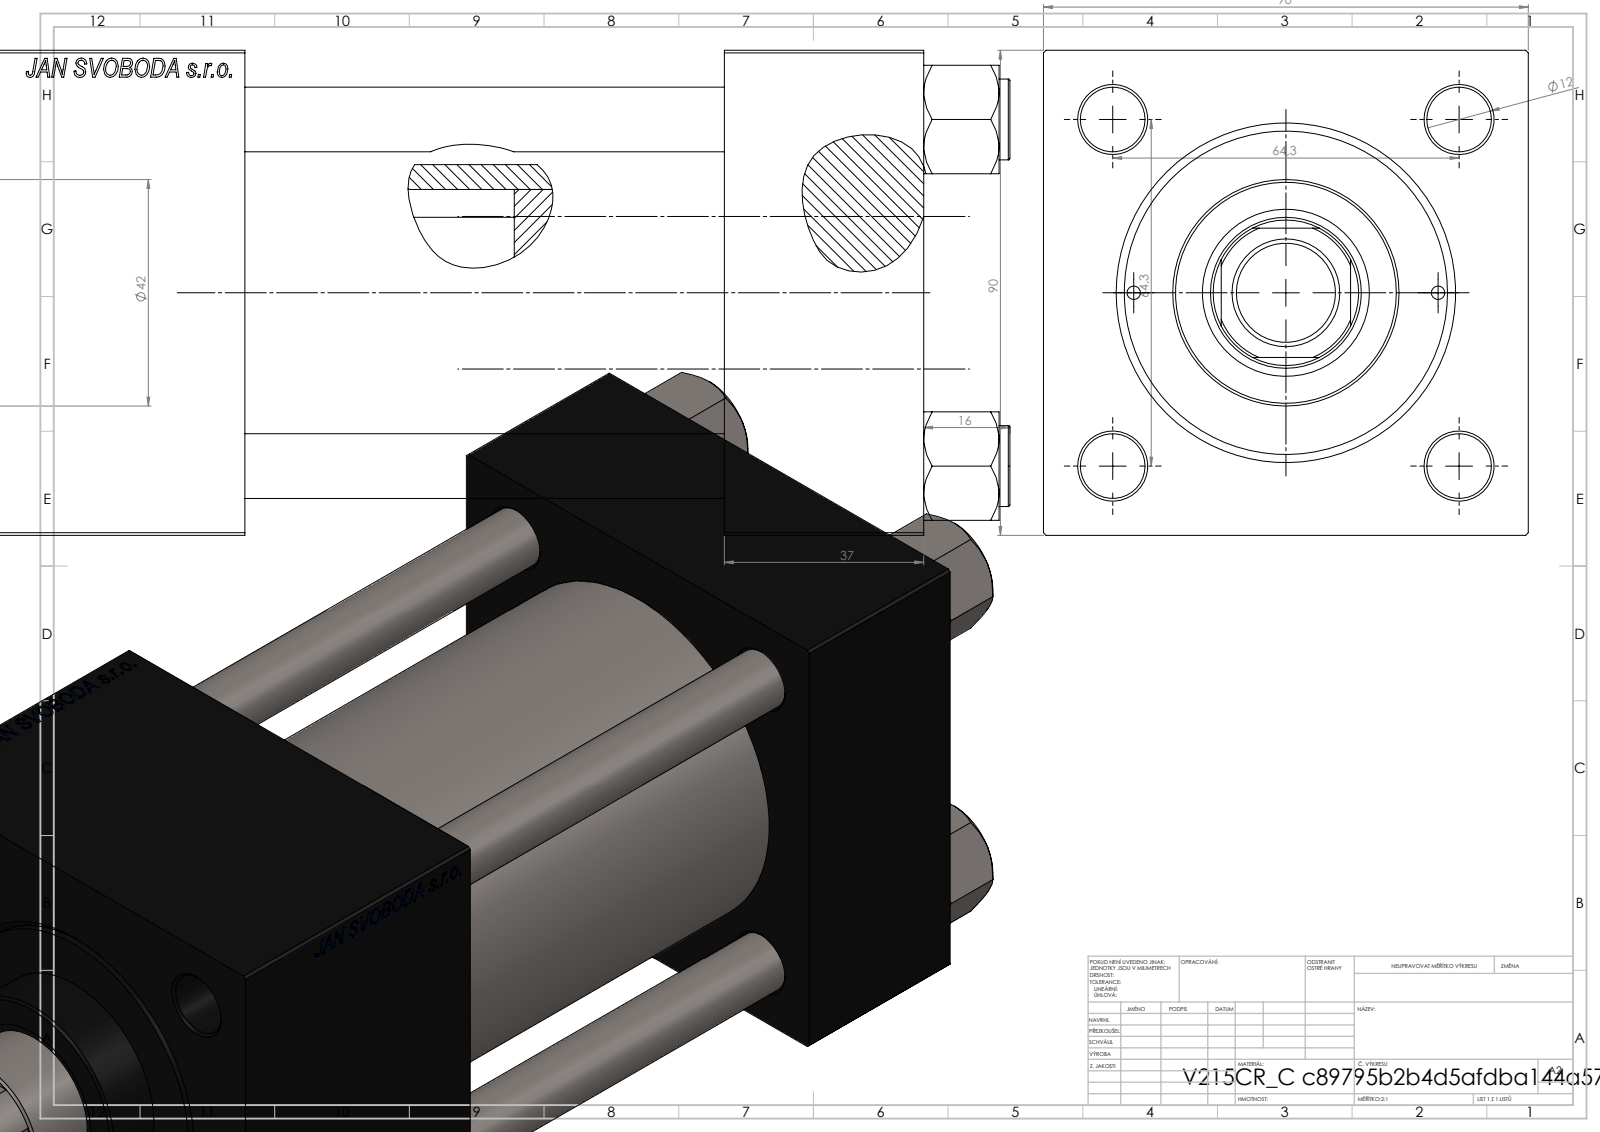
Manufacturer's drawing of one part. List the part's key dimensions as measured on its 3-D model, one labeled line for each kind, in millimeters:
Part name (STEP PRODUCT): ROD_END_AH; NUT_M5_C; V215_VC_A; V215CR_C_TYCINKA (+2 more)
STEP written by: SolidWorks 2019 (CONFIG_CONTROL_DESIGN)
Units: millimetres
Bodies: 12 solids, 1168 faces (532 planar, 94 cylindrical, 542 other)
Overall size (bounding box): 261 × 90 × 90
Volume: 1 006 000 mm³ · Surface area: 201 244 mm²
Round holes (diameter × count): ⌀12 ×4, ⌀2.5 ×2, ⌀7 ×2, ⌀20.96 ×2, ⌀30 ×2, ⌀18.5 ×1, ⌀28 ×1, ⌀31 ×1, ⌀50 ×1, ⌀60 ×1, ⌀63 ×1
Round bosses / shafts (diameter × count): ⌀15 ×4, ⌀69 ×1, ⌀42 ×1, ⌀20 ×1, ⌀18 ×1
Partial cylindrical surfaces — rounded edges, fillets, slot ends (radius × count): R13.5 ×1
Main face-to-face distances: 90, 37, 185, 148, 126, 89, 59, 156.3, 119.3, 30.3
Hole centre spacings: 32.39, 45.47, 64.3, 68.42, 28.25, 90.93, 56.5, 127.5
